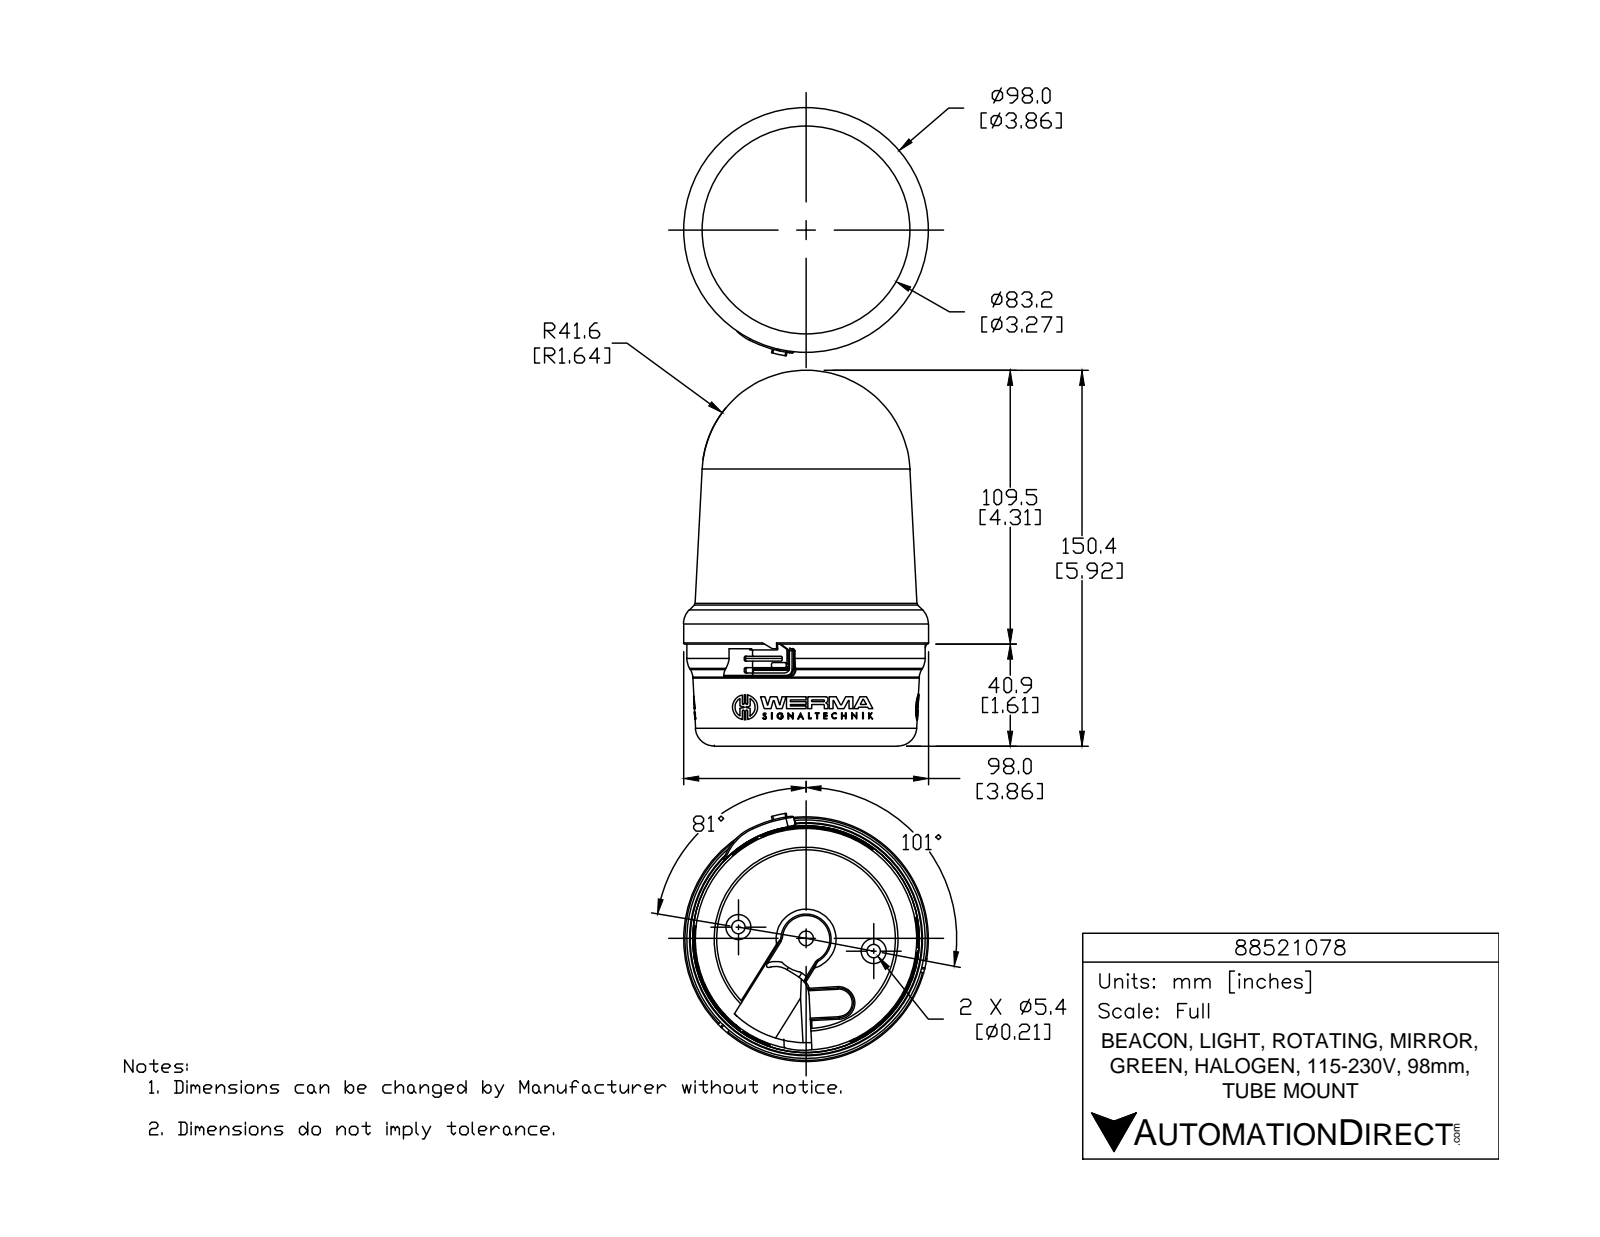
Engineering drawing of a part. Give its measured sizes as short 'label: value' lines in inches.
name: 88521078
written by: SolidWorks 2015 (AUTOMOTIVE_DESIGN)
unit: in
bodies: 1 solid, 1006 faces (554 planar, 189 cylindrical, 263 other)
size: 7.914 × 3.912 × 3.858
volume: 54.7 in³; area: 91.39 in²
holes: 3× ⌀0.078, 1× ⌀1.013, 1× ⌀1.024
bosses: 3× ⌀0.452, 3× ⌀0.113, 1× ⌀3.858, 1× ⌀1.409, 1× ⌀1.261
rounds: 12× R0.02, 9× R0.007, 6× R0.007, 6× R0.016, 6× R0.016, 6× R0.016, 6× R0.262, 3× R0.006
face distances: 2.214, 0.462, 2.676, 0.335, 0.127, 2.548, 2.603, 2.476, 2.141, 0.073
